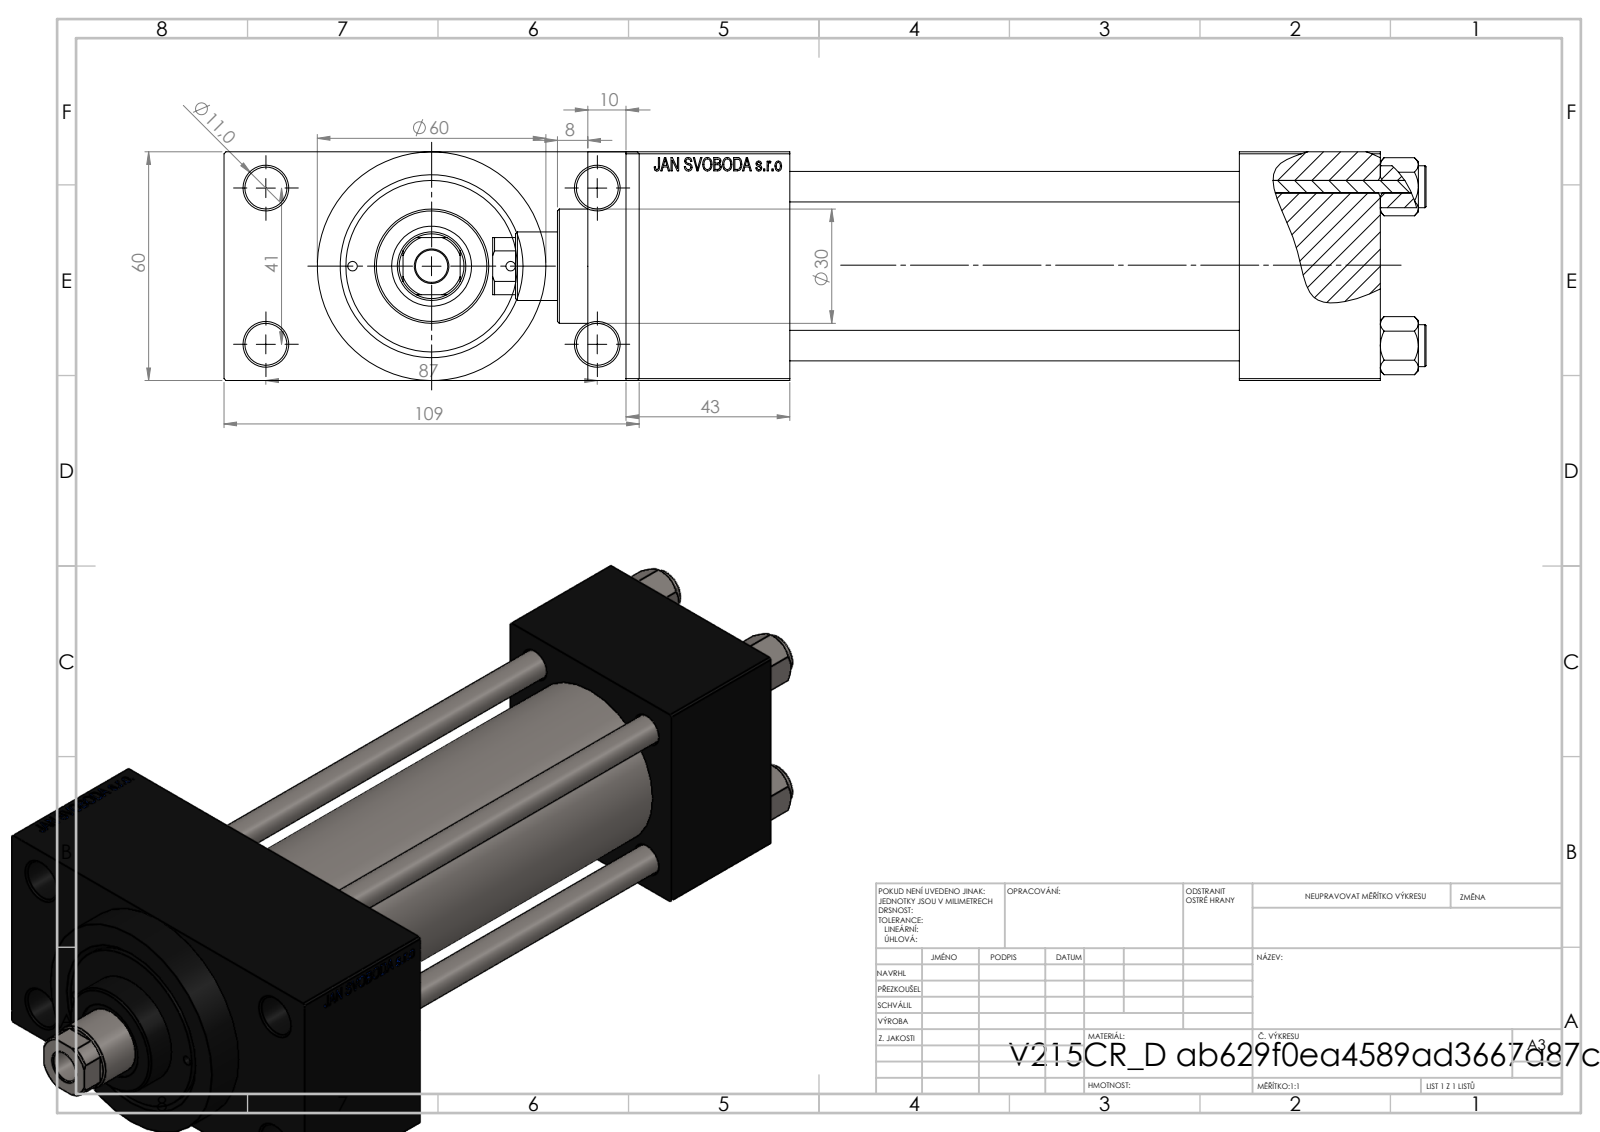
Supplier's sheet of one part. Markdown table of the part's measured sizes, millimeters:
| quantity | value |
| --- | --- |
| part name | V215CR_D_TYCINKA; NUT_M5_D; V215CR_D_Body; V215_VC_A (+1 more) |
| STEP written by | SolidWorks 2019 (CONFIG_CONTROL_DESIGN) |
| units | millimeters |
| bodies | 11 solids, 1112 faces (500 planar, 92 cylindrical, 520 other) |
| overall size | 245 × 109 × 60 |
| volume | 563 958 mm³ |
| surface area | 148 139 mm² |
| round holes (diameter × count) | 8 × 4, 11 × 4, 2.5 × 2, 7 × 2, 16.66 × 2, 24 × 2, 8.5 × 1, 18 × 1, 21 × 1, 31 × 1, 40 × 1, 45 × 1 |
| round bosses / shafts (diameter × count) | 11 × 4, 60 × 1, 46 × 1, 30 × 1 |
| partial cylindrical surfaces (radius × count) | 8.5 × 1 |
| main face-to-face distances | 60, 118, 24.5, 84.5, 37, 155, 198, 161, 43, 164.74 |
| hole center spacings | 20.85, 22.65, 29.49, 30.62, 41.7, 46.53, 47.15, 48.09 |
